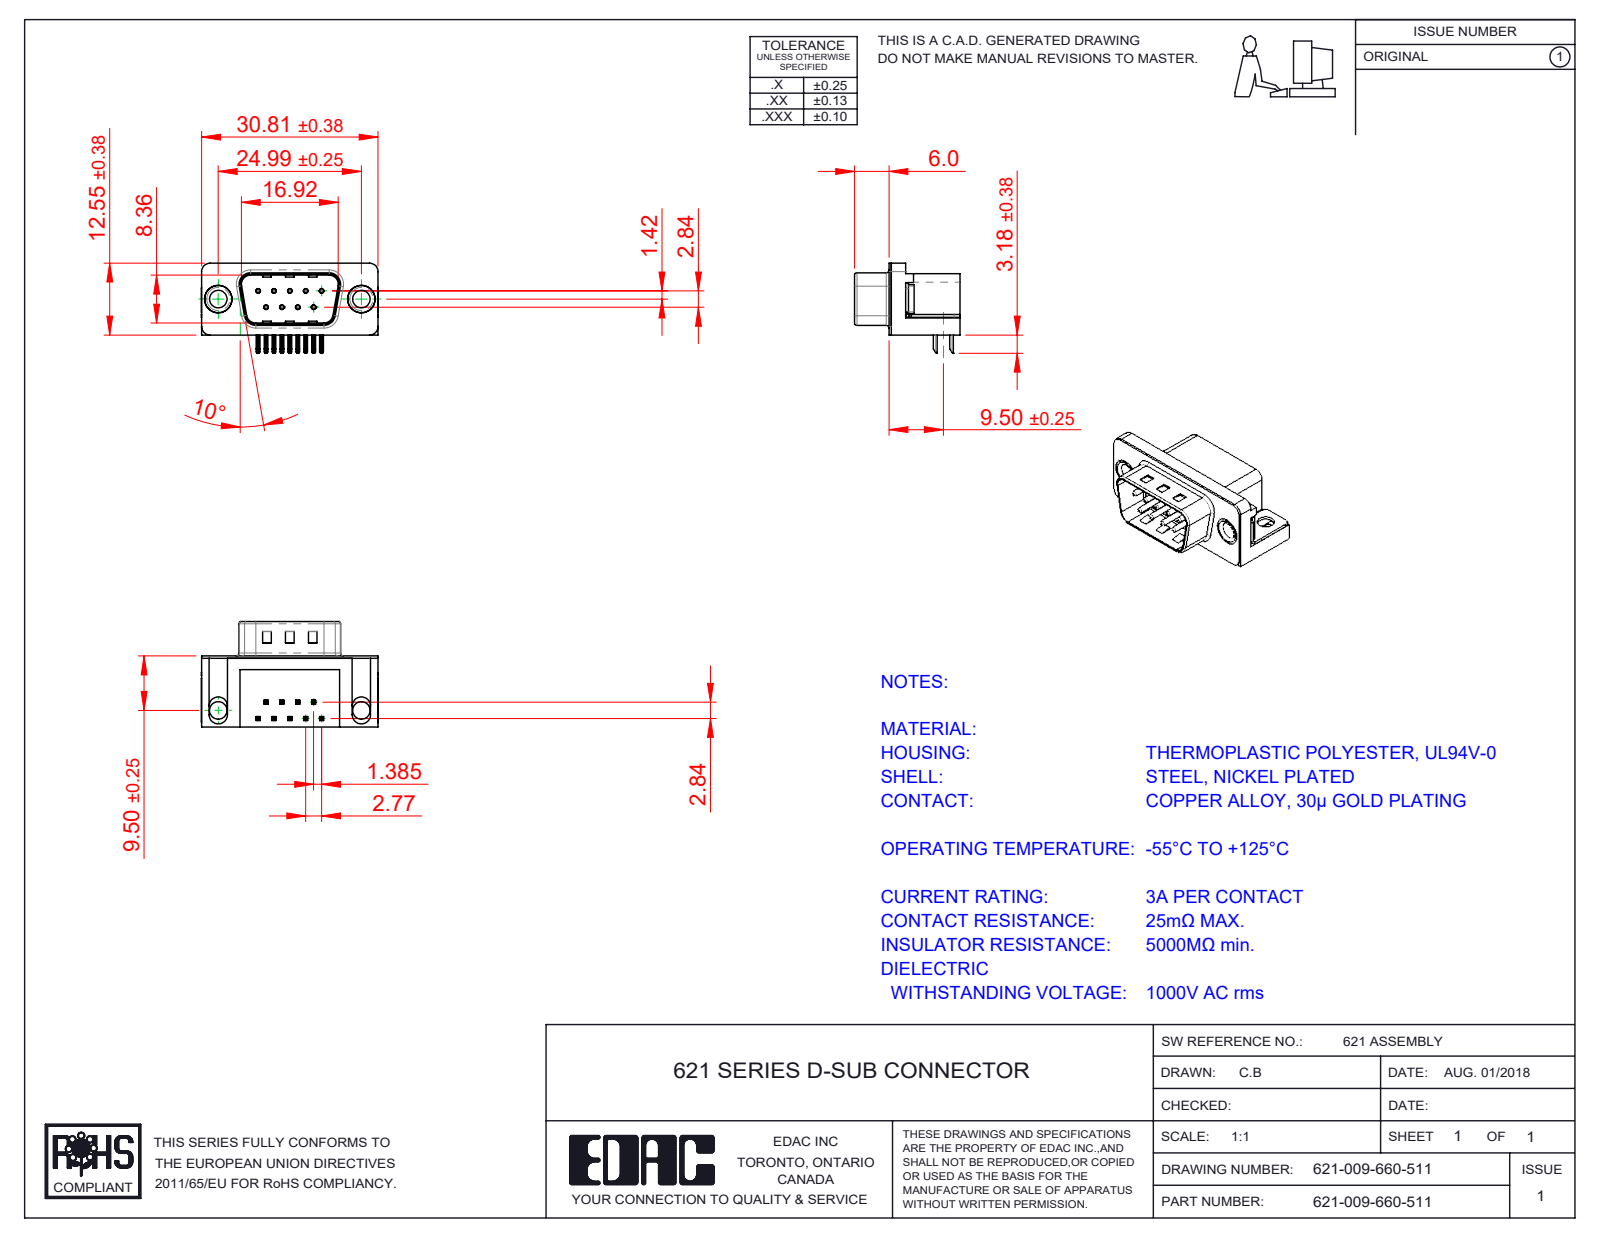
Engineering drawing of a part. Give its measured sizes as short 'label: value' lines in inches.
name: 621 Thru Hole Rivet; 621 Contact Top; 621 Contact Bottom; 621-009-660-511 (+3 more)
written by: SolidWorks 2016 (CONFIG_CONTROL_DESIGN)
unit: in
bodies: 15 solids, 949 faces (571 planar, 297 cylindrical, 81 other)
size: 1.216 × 0.724 × 0.619
volume: 0.197 in³; area: 6.795 in²
holes: 9× ⌀0.014, 9× ⌀0.031, 4× ⌀0.12, 2× ⌀0.157, 2× ⌀0.189, 2× ⌀0.197
bosses: 9× ⌀0.03, 2× ⌀0.193, 2× ⌀0.187, 2× ⌀0.152
rounds: 44× R0.01, 18× R0.005, 16× R0.039, 9× R0.02, 8× R0.059, 8× R0.063, 4× R0.035, 4× R0.079
face distances: 0.016, 0.472, 0.488, 0.407, 0.02, 0.114, 0.374, 0.098, 0.083, 0.014
hole spacings: 0.124, 0.109, 0.218, 0.198, 0.198, 0.327, 0.294, 0.295
